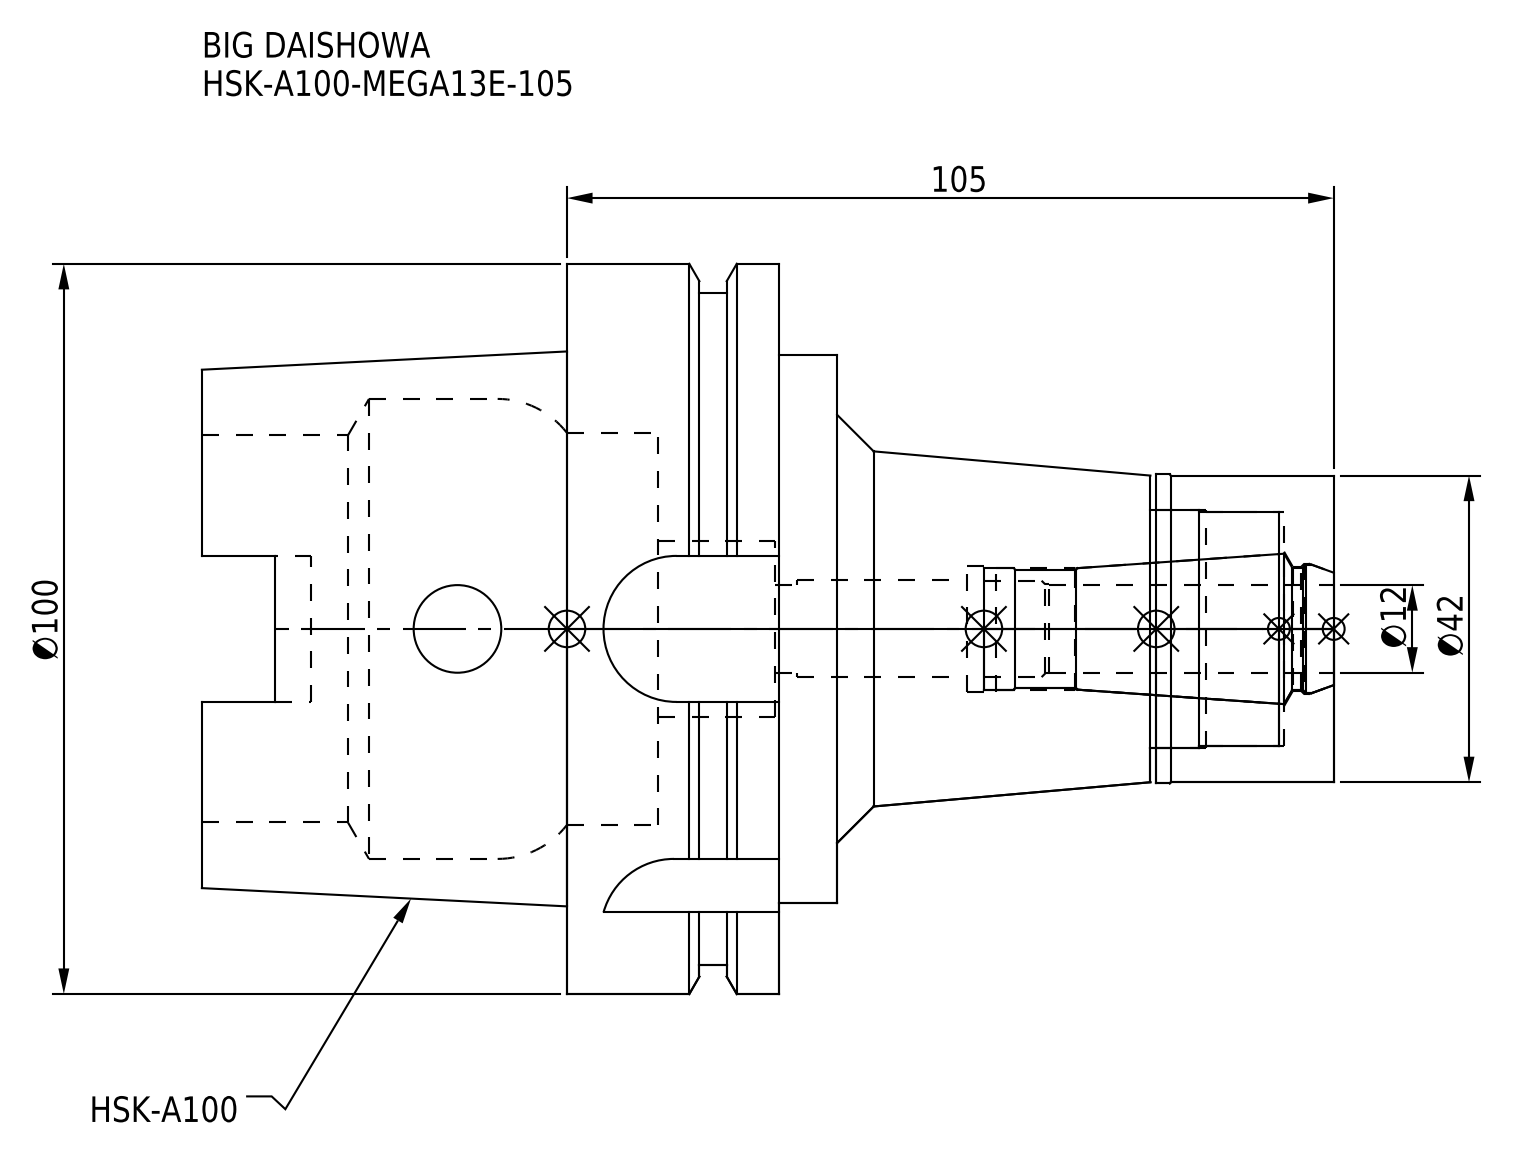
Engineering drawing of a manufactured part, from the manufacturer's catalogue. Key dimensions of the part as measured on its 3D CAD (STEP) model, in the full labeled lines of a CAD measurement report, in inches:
Part name (STEP PRODUCT): HSK-A100-MEGA13E-105; HSK-A100-MEGA13E-105_1.stp; DXF_TEMP_ASSY_ASM_4_ASM.stp; HSK-A100-MEGA13E-105-120-FreeParts (+3 more)
STEP written by: SolidWorks 2019 (CONFIG_CONTROL_DESIGN)
Units: inches
Bodies: 2 solids, 126 faces (42 planar, 56 cylindrical, 28 other)
Overall size (bounding box): 6.102 × 3.937 × 3.937
Volume: 23.15 in³ · Surface area: 108.3 in²
Round holes (diameter × count): ⌀0.472 ×2, ⌀0.524 ×1, ⌀0.654 ×1, ⌀0.669 ×1, ⌀0.677 ×1, ⌀0.705 ×1, ⌀0.945 ×1, ⌀1.26 ×1, ⌀1.28 ×1, ⌀2.087 ×1, ⌀2.118 ×1, ⌀2.48 ×1
Round bosses / shafts (diameter × count): ⌀3.937 ×1, ⌀3.622 ×1, ⌀2.953 ×1, ⌀1.665 ×1, ⌀1.654 ×1
Partial cylindrical surfaces — rounded edges, fillets, slot ends (radius × count): R0.192 ×4, R0.394 ×4
Main face-to-face distances: 1.142, 0.652, 0.49, 0.315, 0.967, 1.457, 2.677, 2.992, 3.644, 4.134
